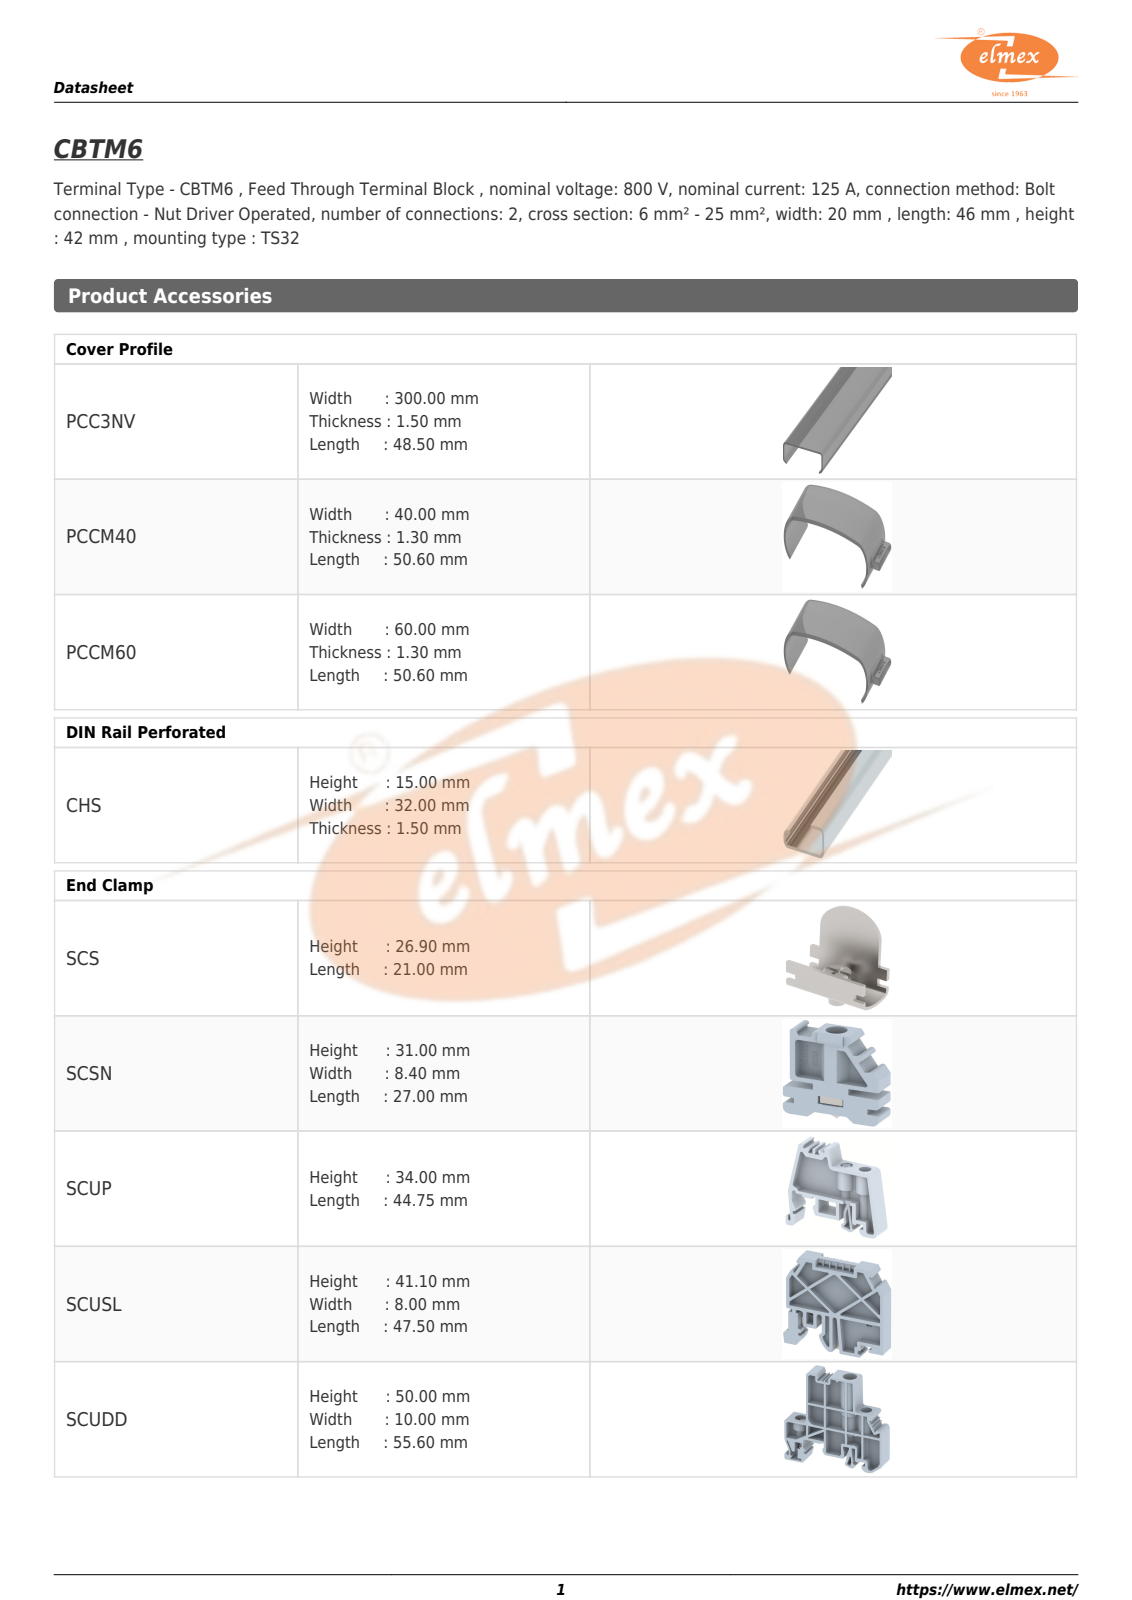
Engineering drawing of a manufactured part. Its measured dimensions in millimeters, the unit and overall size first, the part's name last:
Units: millimetres
Overall size (bounding box): 12.5 × 11.25 × 10
Partial cylindrical surfaces — rounded edges, fillets, slot ends (radius × count): R0.44 ×4, R0.38 ×2, R1 ×2, R0.41 ×1, R0.5 ×1
Main face-to-face distances: 10, 12.5, 11.25, 10.42, 0.83, 7.5, 5, 4.5, 5.92, 6.75
Volume: 1 046 mm³ · Surface area: 712 mm²
Bodies: 1 solid, 44 faces (34 planar, 10 cylindrical, 0 other)
STEP written by: ST-DEVELOPER v16 (AUTOMOTIVE_DESIGN)
